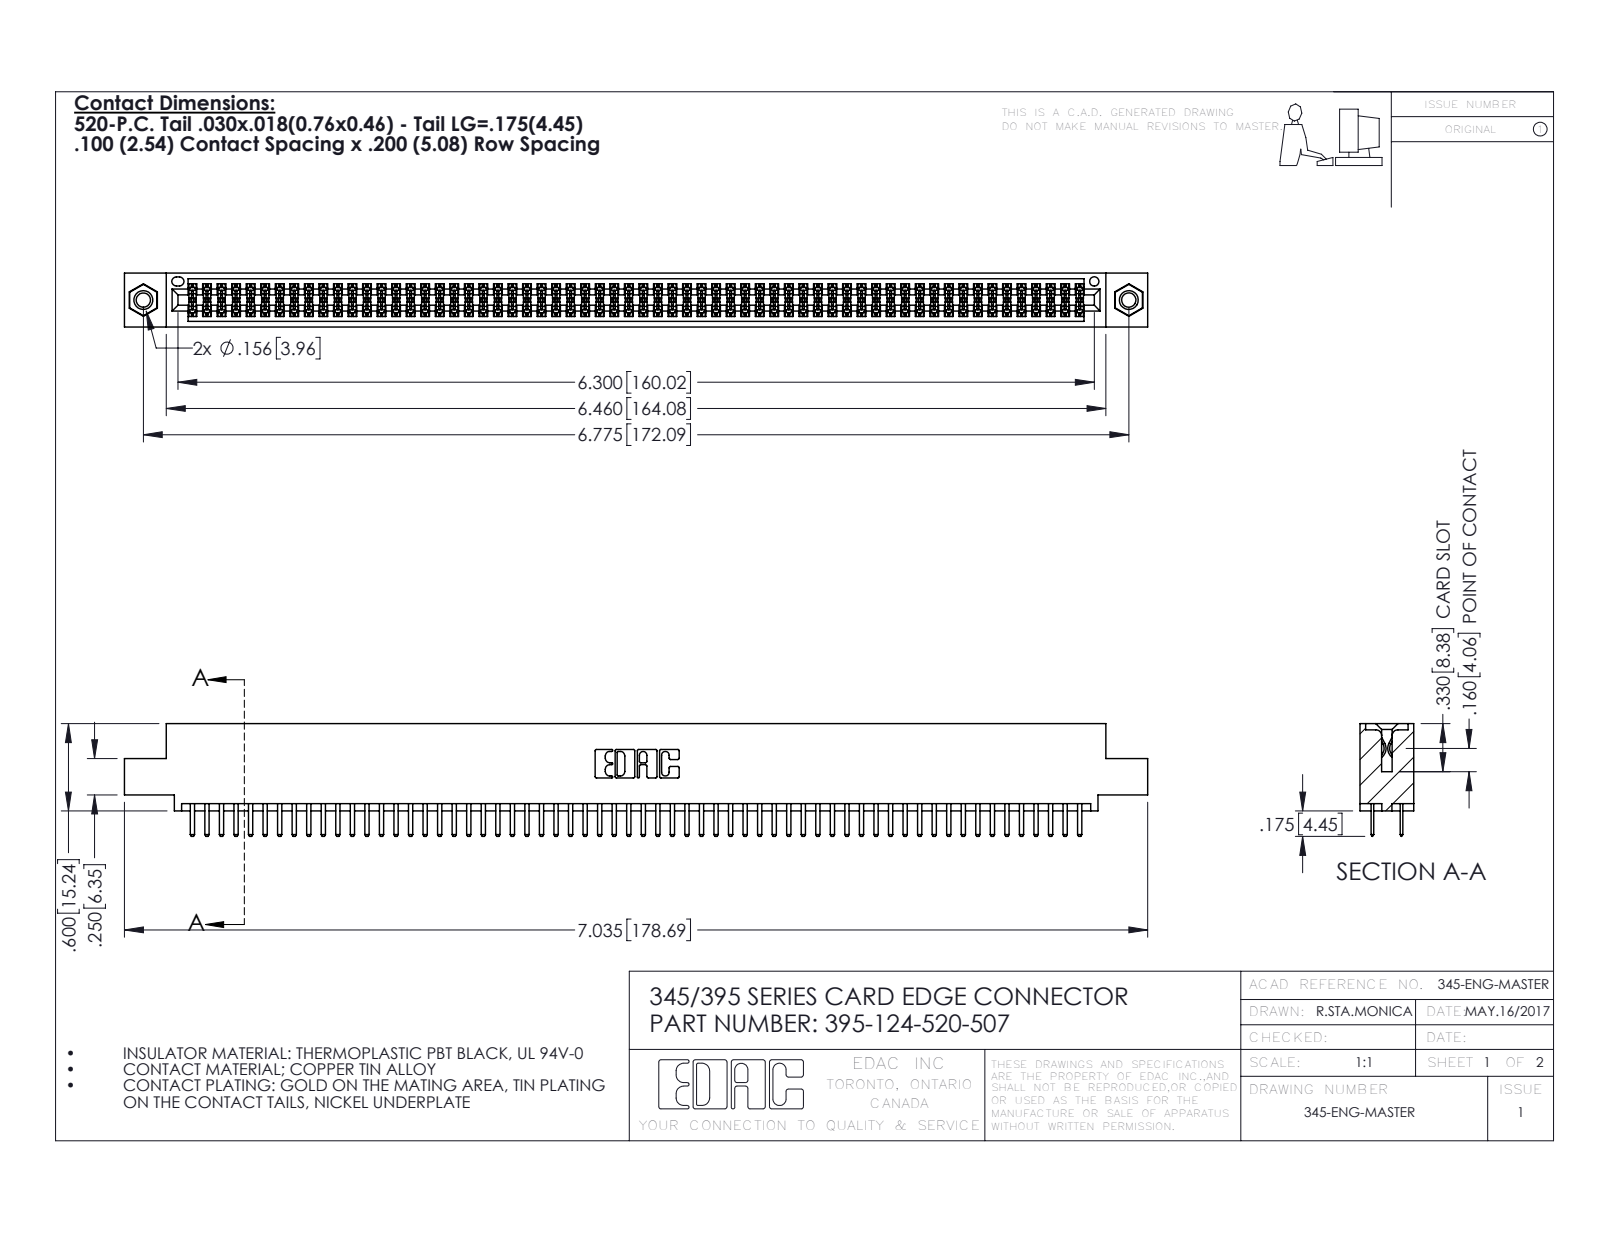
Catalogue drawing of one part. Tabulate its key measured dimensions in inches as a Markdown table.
| quantity | value |
| --- | --- |
| part name | 345 Part_0.110 Offset - 0.156 Dia-TI; 345-250-001_345-250-005-103; 345-292-001_345-293-120; 395-124-520-507 |
| STEP written by | SolidWorks 2016 (CONFIG_CONTROL_DESIGN) |
| units | inches |
| bodies | 127 solids, 6886 faces (4456 planar, 2414 cylindrical, 16 other) |
| overall size | 7.035 × 0.775 × 0.37 |
| volume | 1.062 in³ |
| surface area | 40.48 in² |
| round holes (diameter × count) | 0.098 × 2, 0.125 × 2, 0.156 × 2, 0.064 × 1 |
| round bosses / shafts (diameter × count) | 0.155 × 2 |
| partial cylindrical surfaces (radius × count) | 0.006 × 186, 0.01 × 128, 0.01 × 22, 0.007 × 6, 0.031 × 6, 0.026 × 3, 0.014 × 2, 0.019 × 2 |
| main face-to-face distances | 0.072, 0.298, 0.2, 0.37, 0.098, 0.272, 0.025, 0.225, 0.022, 0.072 |
| hole center spacings | 0.27, 6.539, 6.775 |
